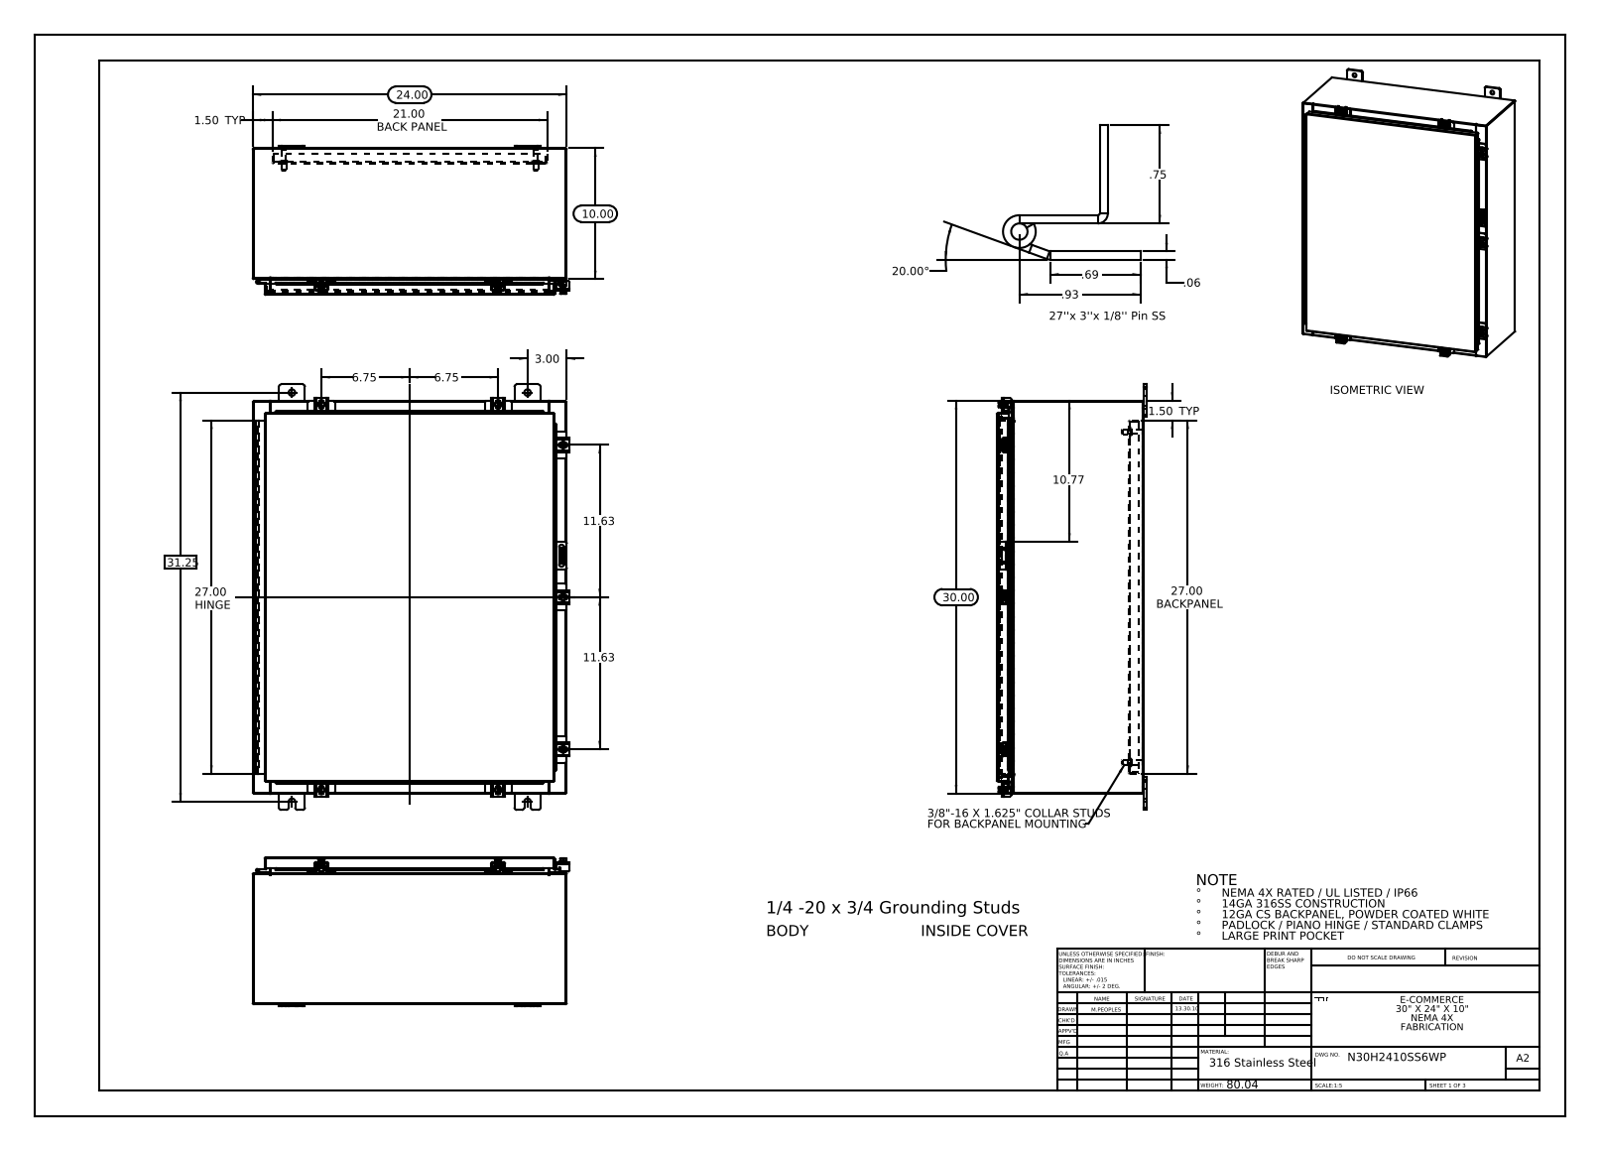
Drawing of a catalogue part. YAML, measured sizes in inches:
part_name: "N30H2410SS6WP Backpanel; N30H2410SS6WP Bottom; N30H2410SS6WP 22101002; N30H2410SS6WP Padlock Hasp (+8 more)"
step_written_by: "SolidWorks 2013 (CONFIG_CONTROL_DESIGN)"
units: inches
bodies: {solids: 54, faces: 2016, planar: 1062, cylindrical: 838, other: 116}
overall_size: [32.5, 24.211, 11.389]
volume: 280.9
surface_area: 7051
round_holes:
  - {diameter: 0.5, count: 8}
  - {diameter: 0.213, count: 7}
  - {diameter: 0.26, count: 7}
  - {diameter: 0.125, count: 2}
  - {diameter: 0.125, count: 1}
round_bosses_or_shafts:
  - {diameter: 0.25, count: 8}
  - {diameter: 0.5, count: 7}
  - {diameter: 0.399, count: 7}
  - {diameter: 0.625, count: 4}
  - {diameter: 0.375, count: 4}
  - {diameter: 0.33, count: 4}
  - {diameter: 0.315, count: 2}
  - {diameter: 0.236, count: 2}
partial_cylinders:
  - {radius: 0.06, count: 34}
  - {radius: 0.013, count: 27}
  - {radius: 0.19, count: 24}
  - {radius: 0.088, count: 21}
  - {radius: 0.12, count: 14}
  - {radius: 0.141, count: 14}
  - {radius: 0.05, count: 11}
  - {radius: 0.08, count: 10}
face_to_face_distances: [0.075, 11.126, 11.051, 11.201, 0.104, 23.925, 1, 1.075, 10.051, 10.126]
hole_center_spacings: [27.501, 31.878, 1.858, 2.277, 2.326, 2.423, 3.561, 3.561]
